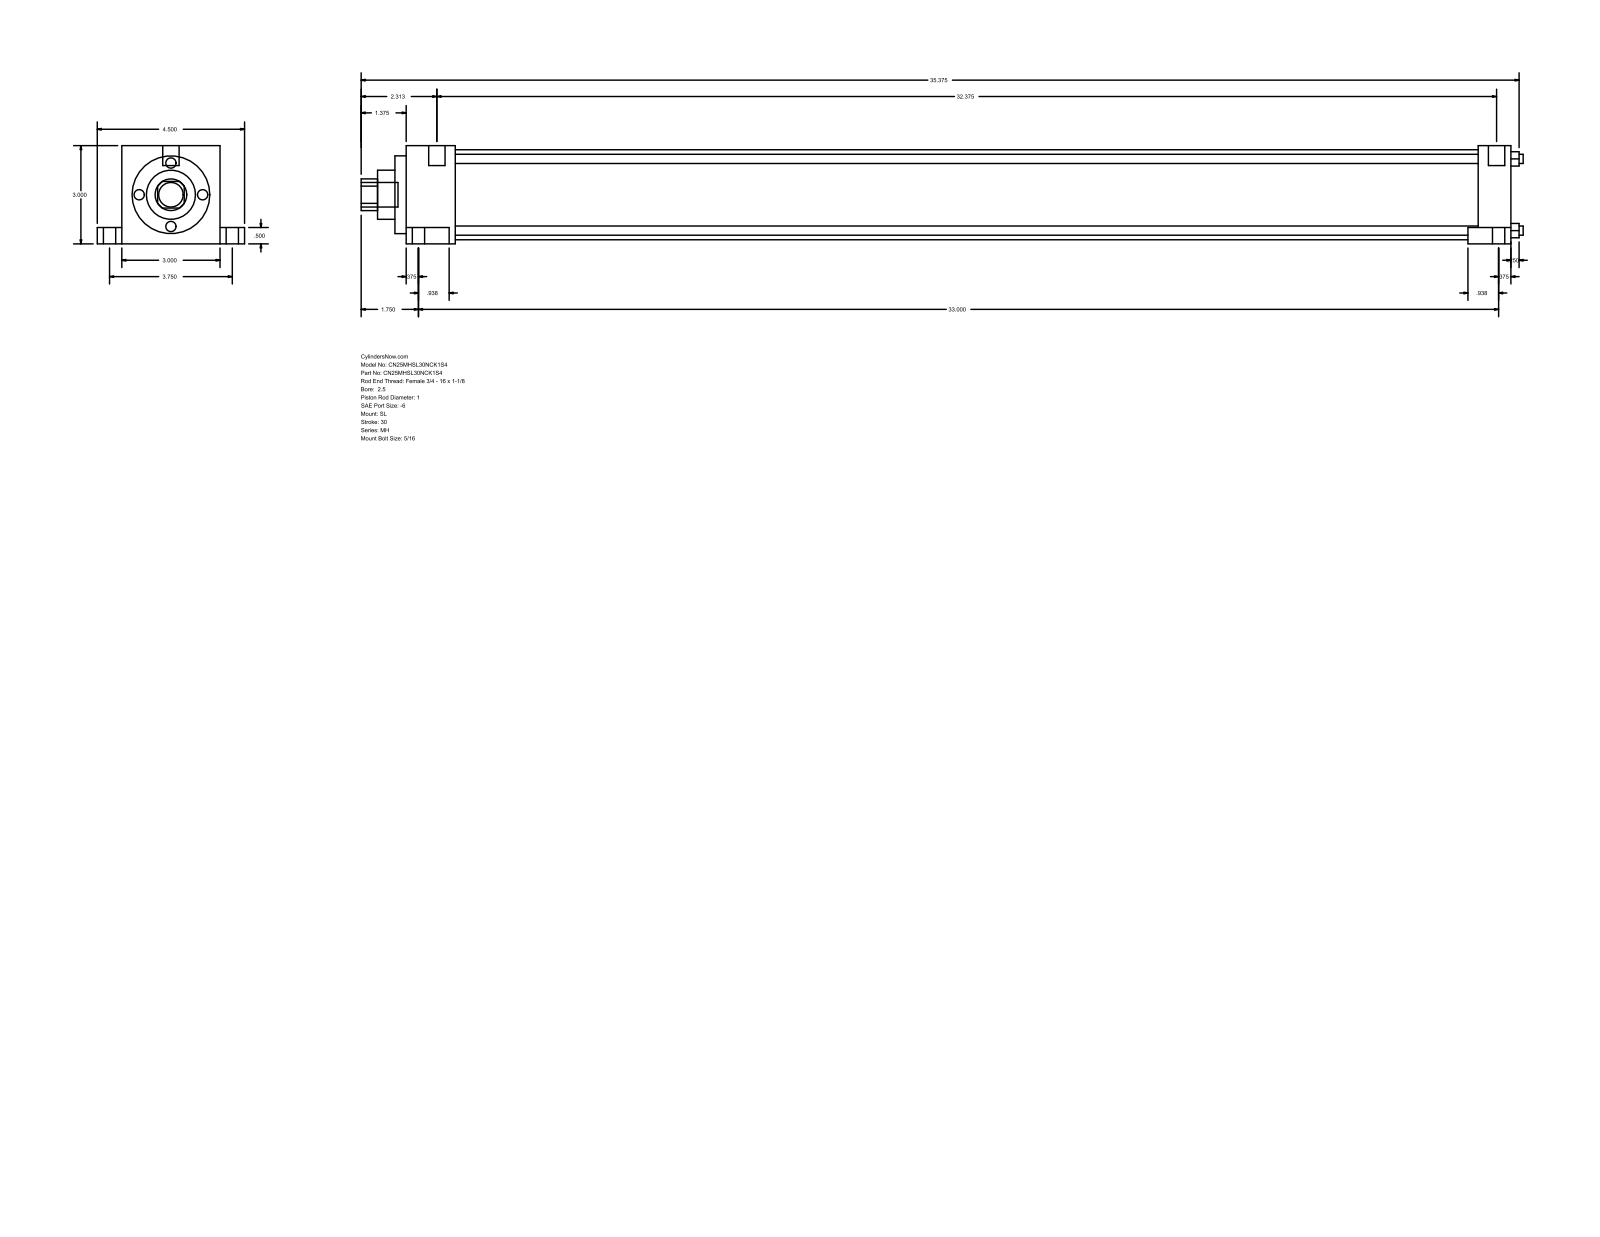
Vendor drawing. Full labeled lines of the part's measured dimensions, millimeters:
Part name (STEP PRODUCT): MH_SL__0250_1
STEP written by: GSSL Pune (CONFIG_CONTROL_DESIGN)
Units: millimetres
Bodies: 0 solids, 86 faces (61 planar, 25 cylindrical, 0 other)
Overall size (bounding box): 901.7 × 114.3 × 76.2
Round holes (diameter × count): ⌀7.14 ×4, ⌀25.4 ×1, ⌀38.1 ×1, ⌀60.33 ×1, ⌀69.85 ×1
Round bosses / shafts (diameter × count): ⌀15.88 ×2, ⌀9.53 ×2, ⌀5.56 ×2, ⌀19.05 ×1, ⌀12.7 ×1
Partial cylindrical surfaces — rounded edges, fillets, slot ends (radius × count): R12.29 ×1
Main face-to-face distances: 76.2, 25.4, 840.58, 865.98, 12.7, 63.5, 19.05, 95.25, 13.49, 854.07
Hole centre spacings: 39.33, 55.62, 78.66
